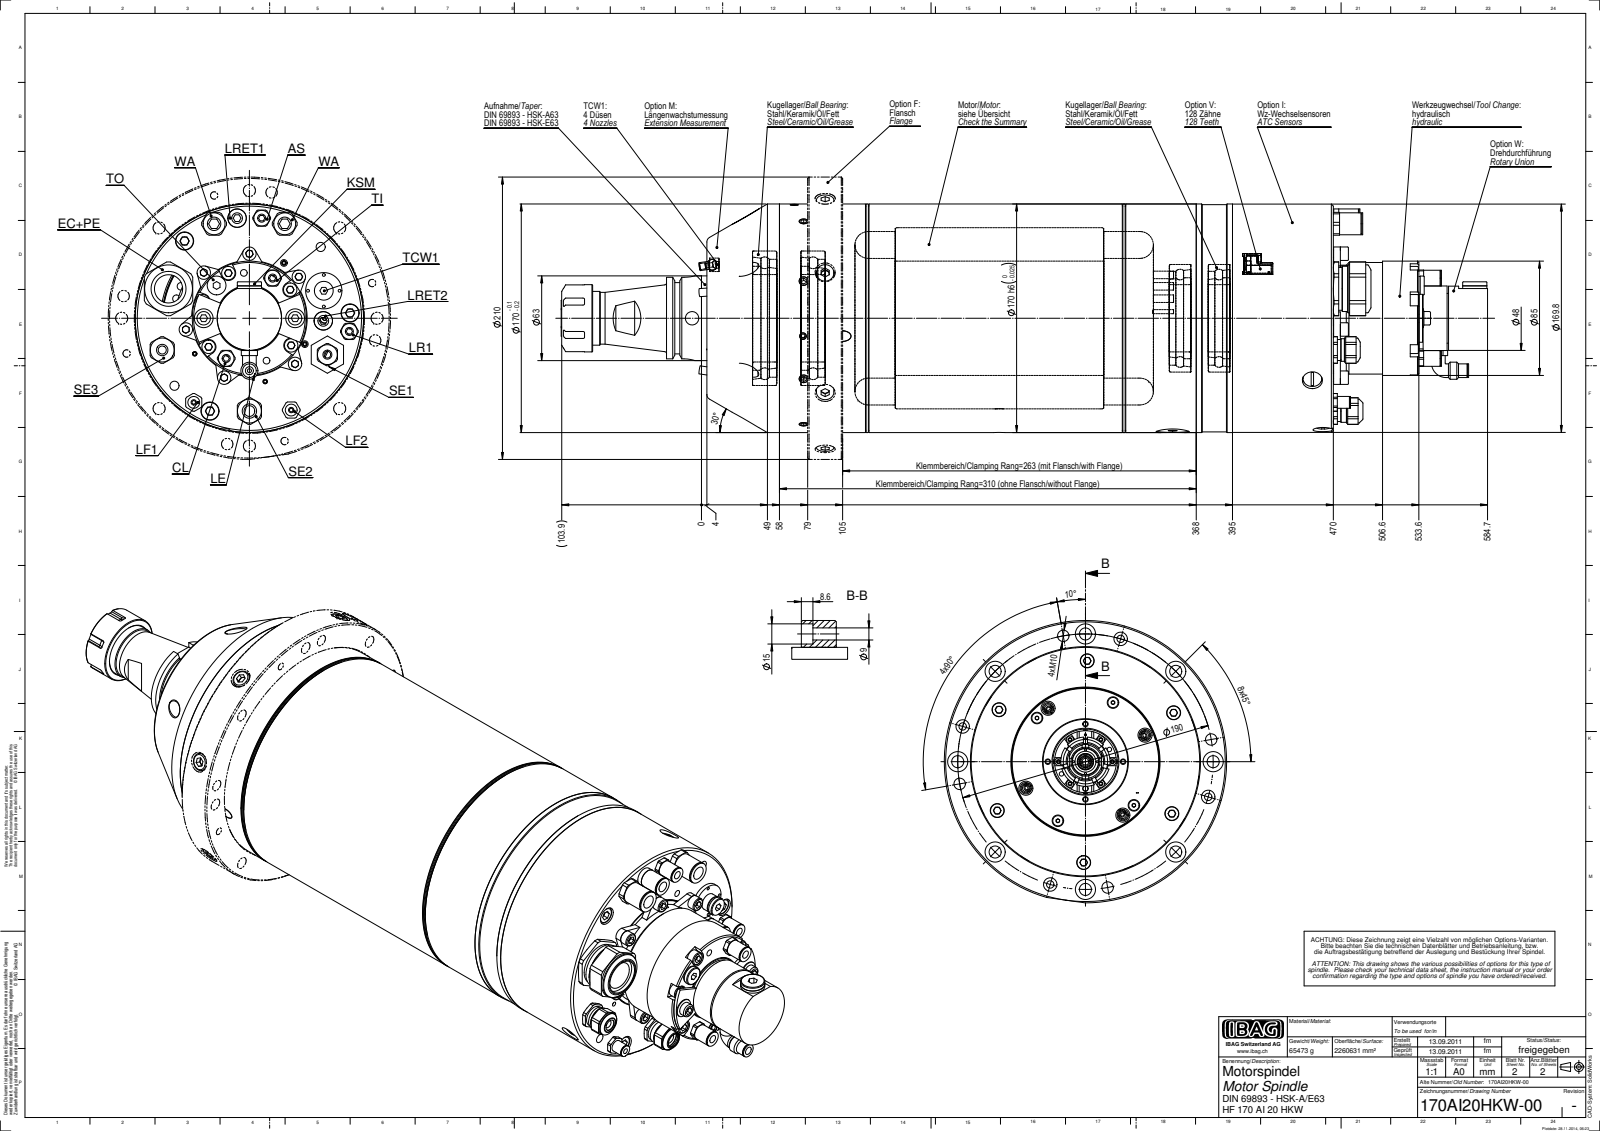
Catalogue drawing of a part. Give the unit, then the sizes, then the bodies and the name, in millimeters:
Units: millimetres
Overall size (bounding box): 683.74 × 170 × 170
Round holes (diameter × count): ⌀6.8 ×12, ⌀6 ×10, ⌀5 ×7, ⌀8.5 ×7, ⌀10.4 ×6, ⌀4.5 ×4, ⌀10 ×4, ⌀15 ×4, ⌀2.1 ×3, ⌀4 ×3, ⌀13.5 ×3, ⌀8 ×2
Round bosses / shafts (diameter × count): ⌀10 ×18, ⌀6 ×8, ⌀14 ×5, ⌀11.7 ×4, ⌀7.64 ×4, ⌀17.8 ×2, ⌀16.79 ×2, ⌀16.3 ×2
Partial cylindrical surfaces — rounded edges, fillets, slot ends (radius × count): R1 ×12, R5.5 ×6, R6.6 ×6, R8 ×4, R9.25 ×2, R9.9 ×2, R6.5 ×1, R13.2 ×1
Main face-to-face distances: 75, 337, 412, 27, 310, 102, 54, 364, 391, 466
Hole centre spacings: 75, 129.91, 16.62, 17.63, 18.28, 27.33, 27.98, 29.81
Bodies: 0 solids, 1371 faces (564 planar, 524 cylindrical, 283 other)
Part name (STEP PRODUCT): 170AI20HKW-00
STEP written by: SolidWorks 2010 (CONFIG_CONTROL_DESIGN)
